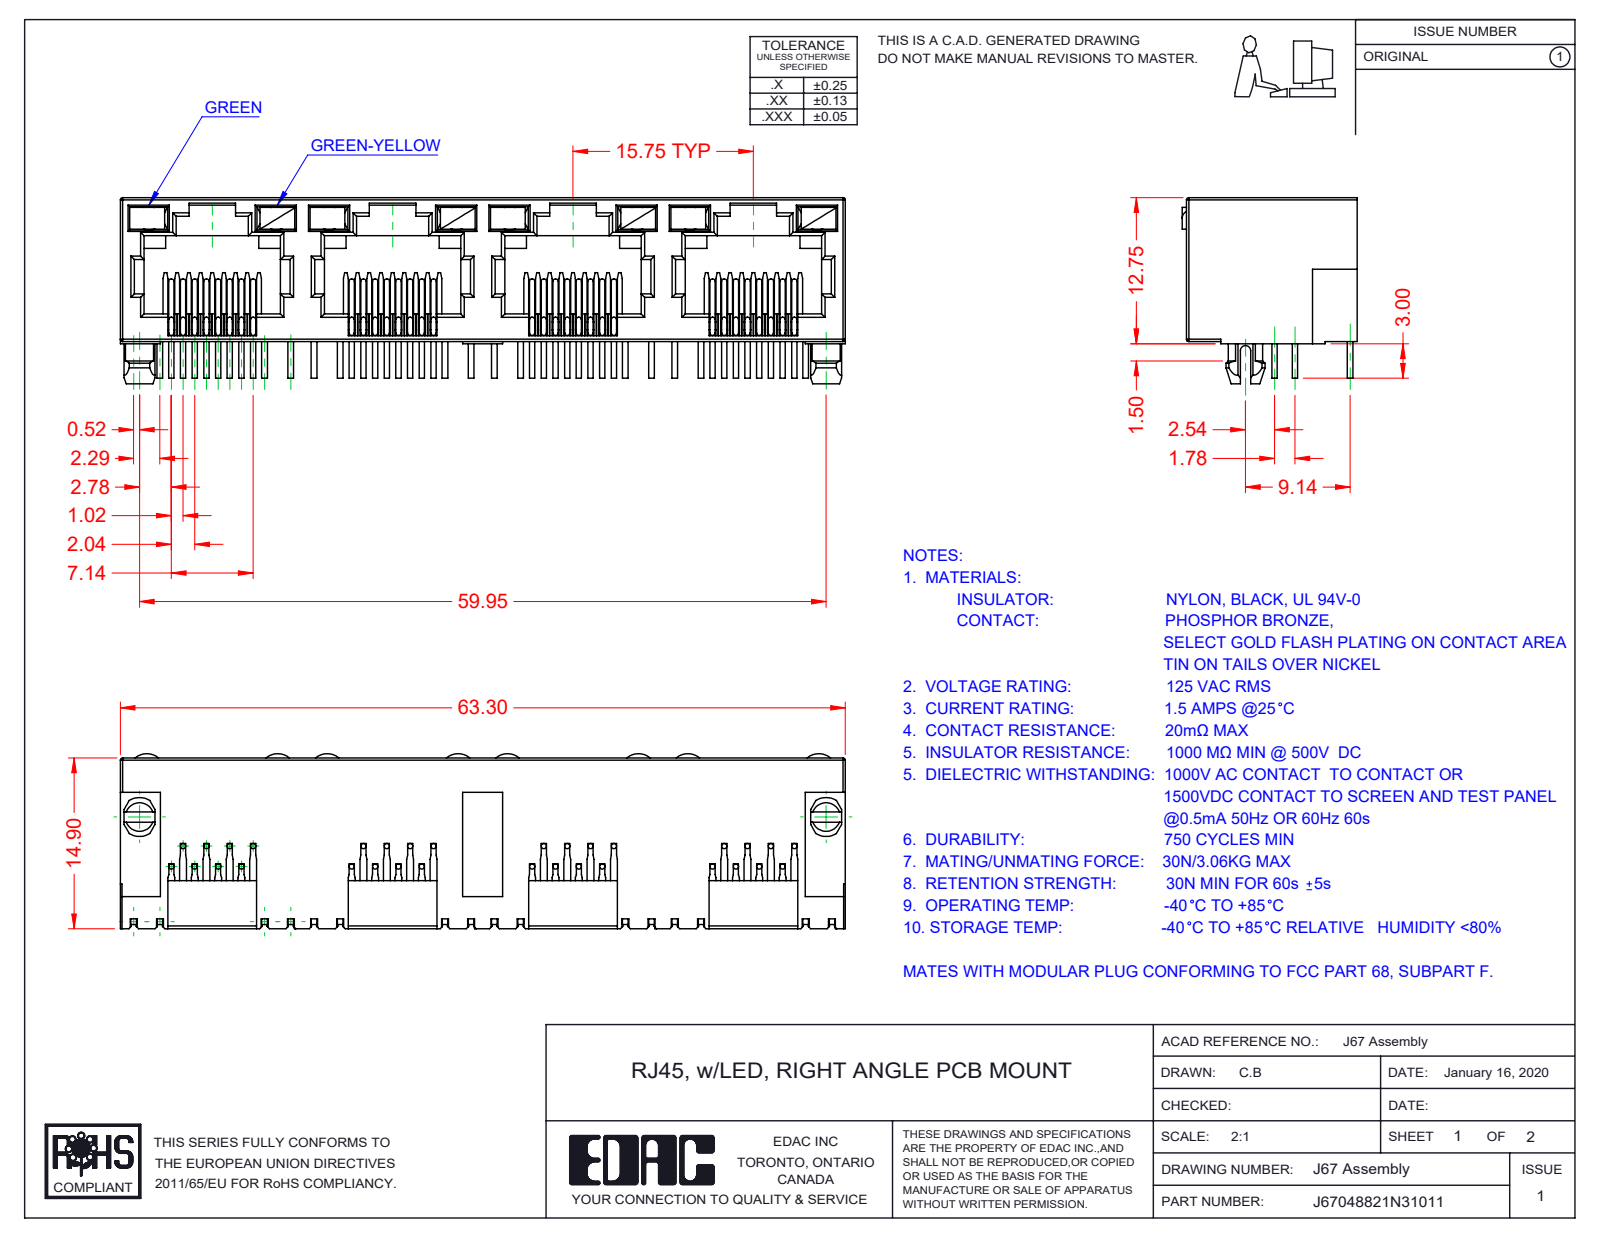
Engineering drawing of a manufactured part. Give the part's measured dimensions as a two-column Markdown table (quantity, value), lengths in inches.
| quantity | value |
| --- | --- |
| part name | 67 Insulator; 67 LED LH_3-Green; 67 Contacts; J67048822N35011 (+1 more) |
| STEP written by | SolidWorks 2016 (CONFIG_CONTROL_DESIGN) |
| units | inches |
| bodies | 41 solids, 2473 faces (1781 planar, 484 cylindrical, 208 other) |
| overall size | 2.492 × 0.64 × 0.602 |
| volume | 0.315 in³ |
| surface area | 17.94 in² |
| round bosses / shafts (diameter × count) | 0.018 × 96 |
| partial cylindrical surfaces (radius × count) | 0.008 × 66, 0.012 × 29, 0.018 × 9, 0.061 × 8, 0.059 × 2, 0.067 × 2, 0.014 × 1, 0.039 × 1 |
| main face-to-face distances | 0.02, 0.494, 0.074, 0.035, 0.394, 0.62, 0.039, 0.055, 0.433, 0.468 |
